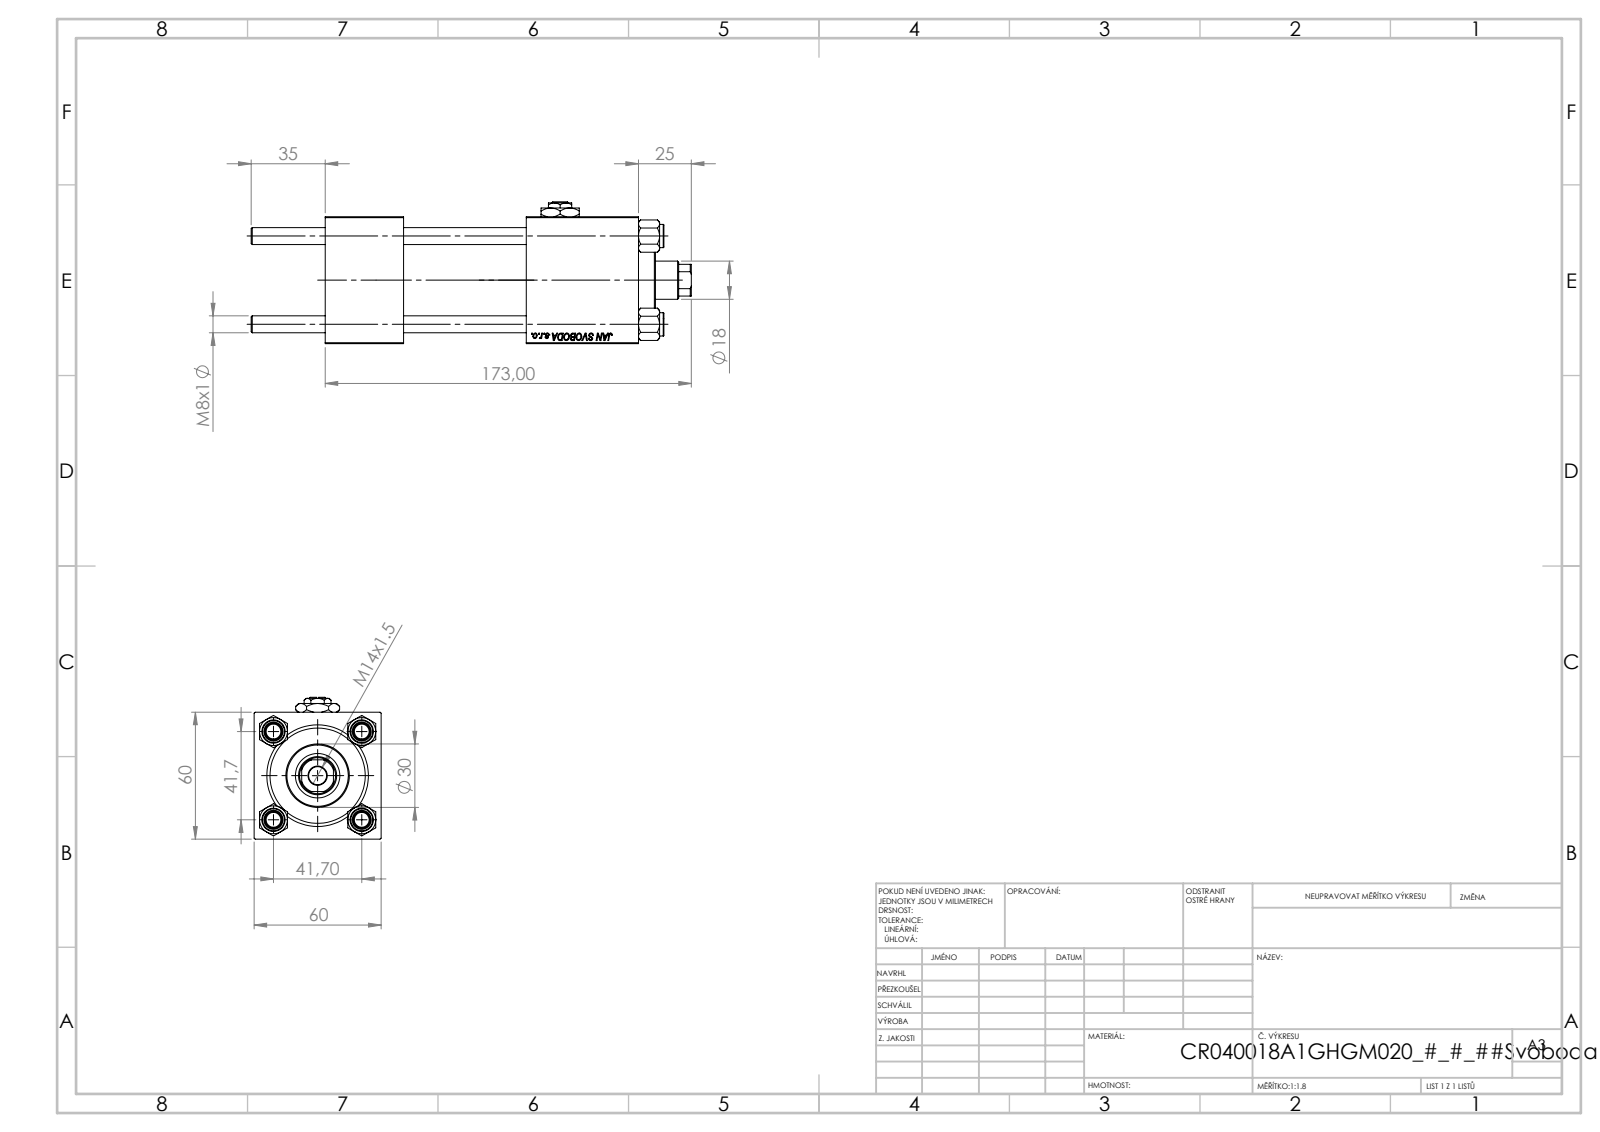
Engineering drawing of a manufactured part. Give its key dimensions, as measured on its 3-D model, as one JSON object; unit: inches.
{"part_name": "V215CR_VCP; NUT_M5; Zatka_pro_OIL_PORT; V215CR_BODY_A (+2 more)", "step_written_by": "SolidWorks 2019 (CONFIG_CONTROL_DESIGN)", "units": "inches", "bodies": {"solids": 12, "faces": 1183, "planar": 545, "cylindrical": 82, "other": 556}, "overall_size": [8.189, 2.638, 2.362], "volume_in3": 25.14, "surface_area_in2": 178.7, "round_holes": [[0.315, 4], [0.276, 2], [0.656, 2], [0.945, 2], [0.335, 1], [0.709, 1], [0.827, 1], [1.22, 1], [1.575, 1], [1.772, 1]], "round_bosses_or_shafts": [[0.433, 4], [1.811, 1], [1.181, 1]], "partial_cylinders_radius": [[0.335, 1]], "face_to_face_distances": [2.362, 1.457, 5.827, 4.37, 2.283, 2.087, 3.74, 4.697, 3.24, 0.957], "hole_center_spacings": [1.161, 1.642, 2.322, 3.642]}
